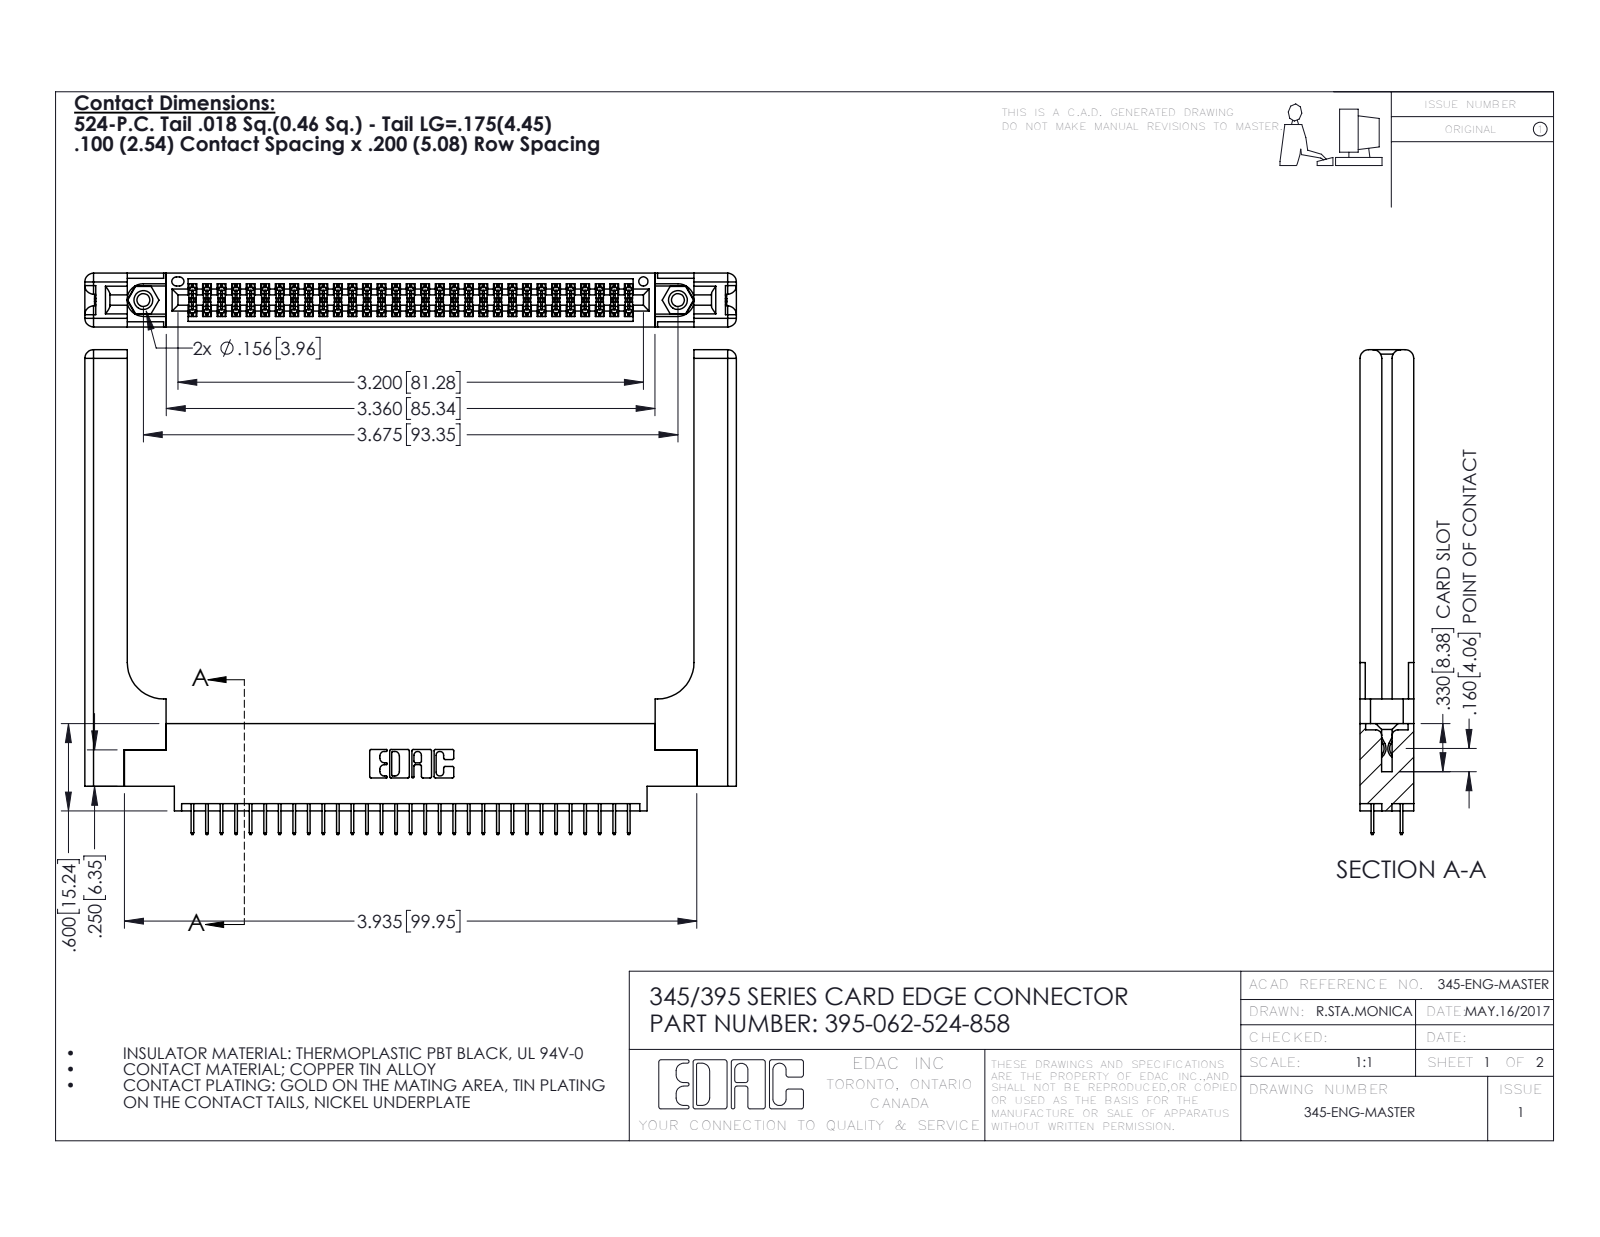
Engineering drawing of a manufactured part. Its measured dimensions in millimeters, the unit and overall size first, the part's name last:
Units: millimetres
Overall size (bounding box): 113.8 × 84.6 × 9.4
Round holes (diameter × count): ⌀2.3 ×2, ⌀3.2 ×2, ⌀4 ×2, ⌀1.6 ×1
Round bosses / shafts (diameter × count): ⌀3.9 ×2
Partial cylindrical surfaces — rounded edges, fillets, slot ends (radius × count): R0.2 ×93, R0.3 ×22, R1.5 ×16, R0.2 ×6, R0.8 ×6, R0.7 ×3, R0.4 ×2, R0.5 ×2
Main face-to-face distances: 9.4, 1.8, 7.6, 5.1, 2.5, 6.9, 0.6, 3.8, 3.8, 5.7
Hole centre spacings: 6.9, 87.4, 93.3
Volume: 19 220 mm³ · Surface area: 20 620 mm²
Bodies: 67 solids, 3734 faces (2650 planar, 1024 cylindrical, 60 other)
Part name (STEP PRODUCT): 345-250-001_345-250-001-102; 345-220-058_345-220-058; 345-292-001_345-293-124; 345 Part_0.170 Offset - 0.156 Dia-TH (+1 more)
STEP written by: SolidWorks 2016 (CONFIG_CONTROL_DESIGN)
